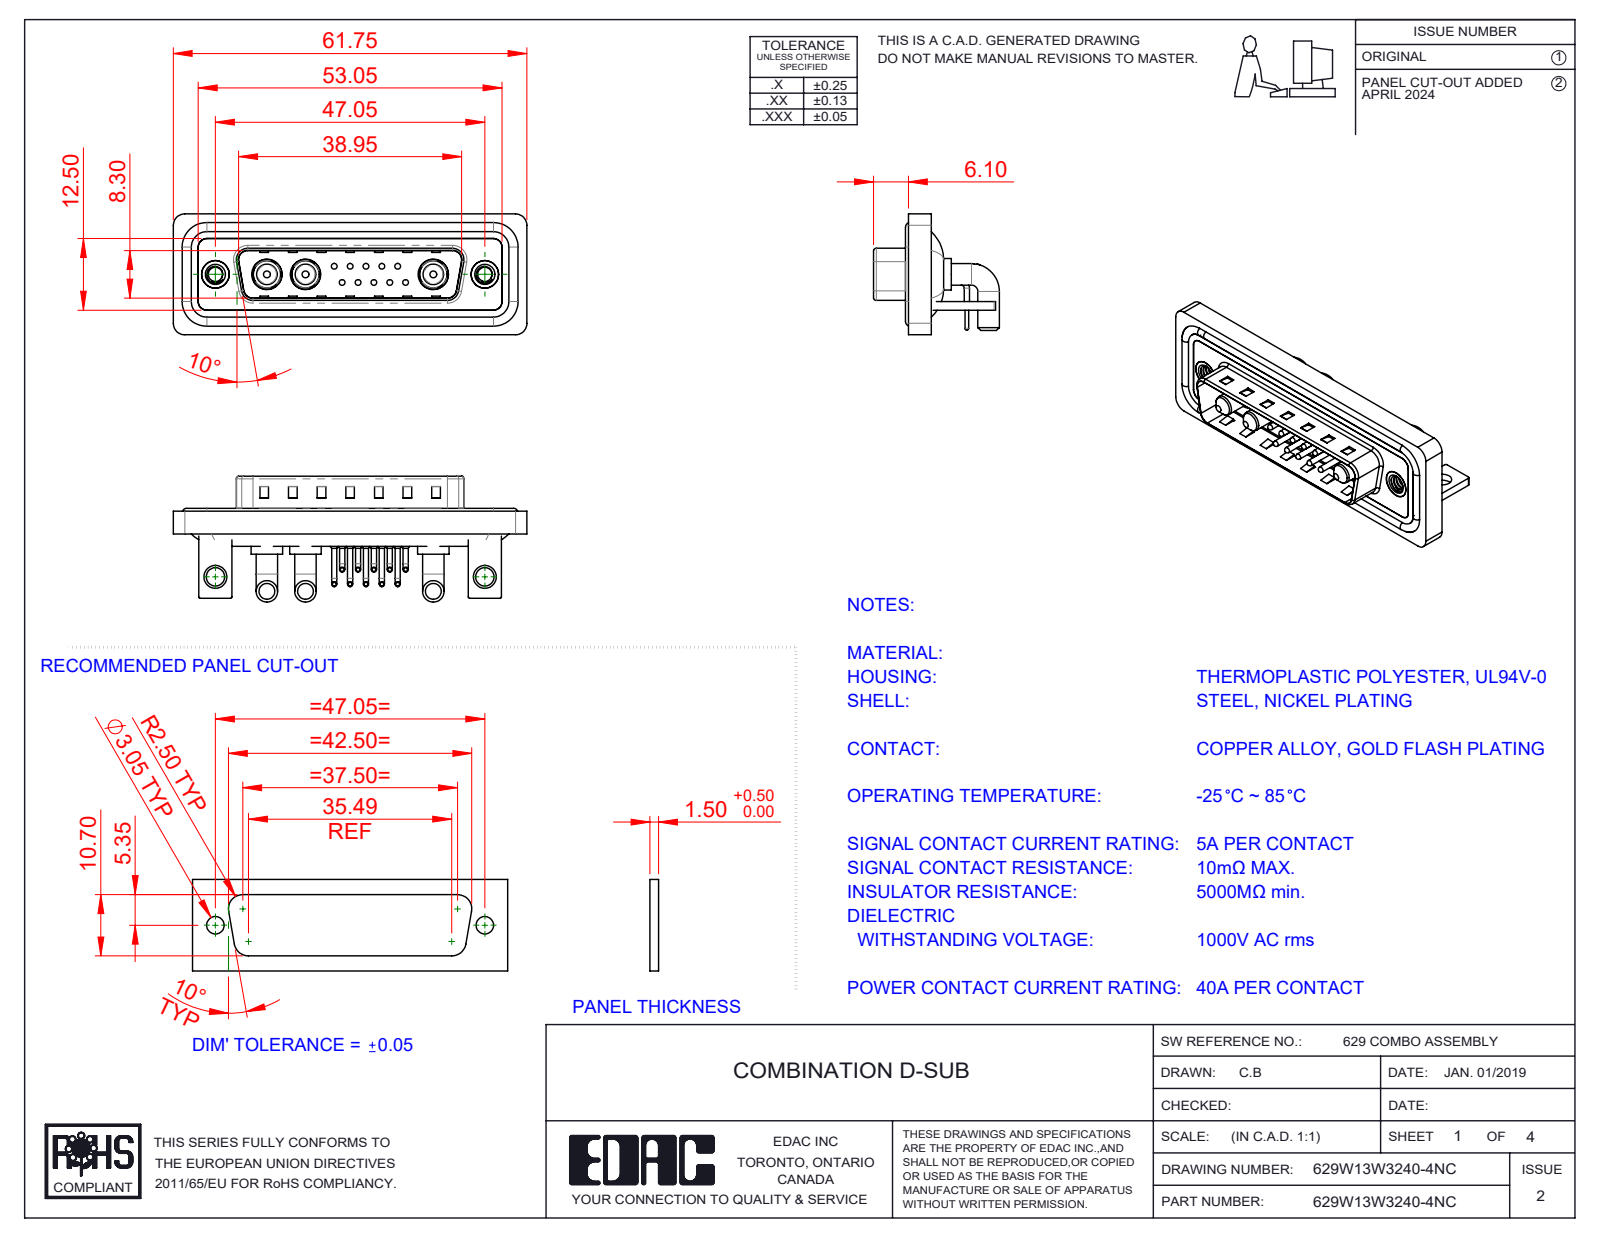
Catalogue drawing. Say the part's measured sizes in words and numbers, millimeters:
The part is named "629Combo Shell Front_25 Contacts; 629Combo Stabilizer Bracket; 629W13W3240-4NC; 629Combo Shell Rear_25 Contacts (+6 more)". Its 3-D file was written by "SolidWorks 2023 (CONFIG_CONTROL_DESIGN)". It is 25 solids with 1750 faces: 899 planar, 629 cylindrical and 222 other. Overall it measures 61.75 by 21.98 by 21.1 millimeters. Its volume is 8 101 cubic millimeters and its surface area 13 216 square millimeters. Round holes: 10 of diameter 0.75, 10 of diameter 1.6, 10 of diameter 2, 3 of diameter 4.85, 3 of diameter 5.3, 2 of diameter 2.5, 2 of diameter 3.2, 2 of diameter 4, 2 of diameter 4.8, 2 of diameter 5. Round bosses or shafts: 20 of diameter 0.9, 10 of diameter 1.5, 10 of diameter 1, 10 of diameter 0.65, 6 of diameter 3.75, 4 of diameter 1.6, 3 of diameter 5.5, 3 of diameter 5.2. Partial cylindrical surfaces (rounded edges, fillets, slot ends): 19 of radius 2, 18 of radius 1.5, 16 of radius 0.25, 10 of radius 1.01, 9 of radius 0.5, 8 of radius 1.6, 4 of radius 0.6, 4 of radius 0.65. The main face-to-face distances are 0.4, 0.8, 1.5, 2.9, 2.1, 1.1, 4.1, 1.6, 3.7, 4.5. The hole center spacings are 3.16, 2.77, 5.04, 5.54, 7.49, 5.03, 8.31, 10.11.
